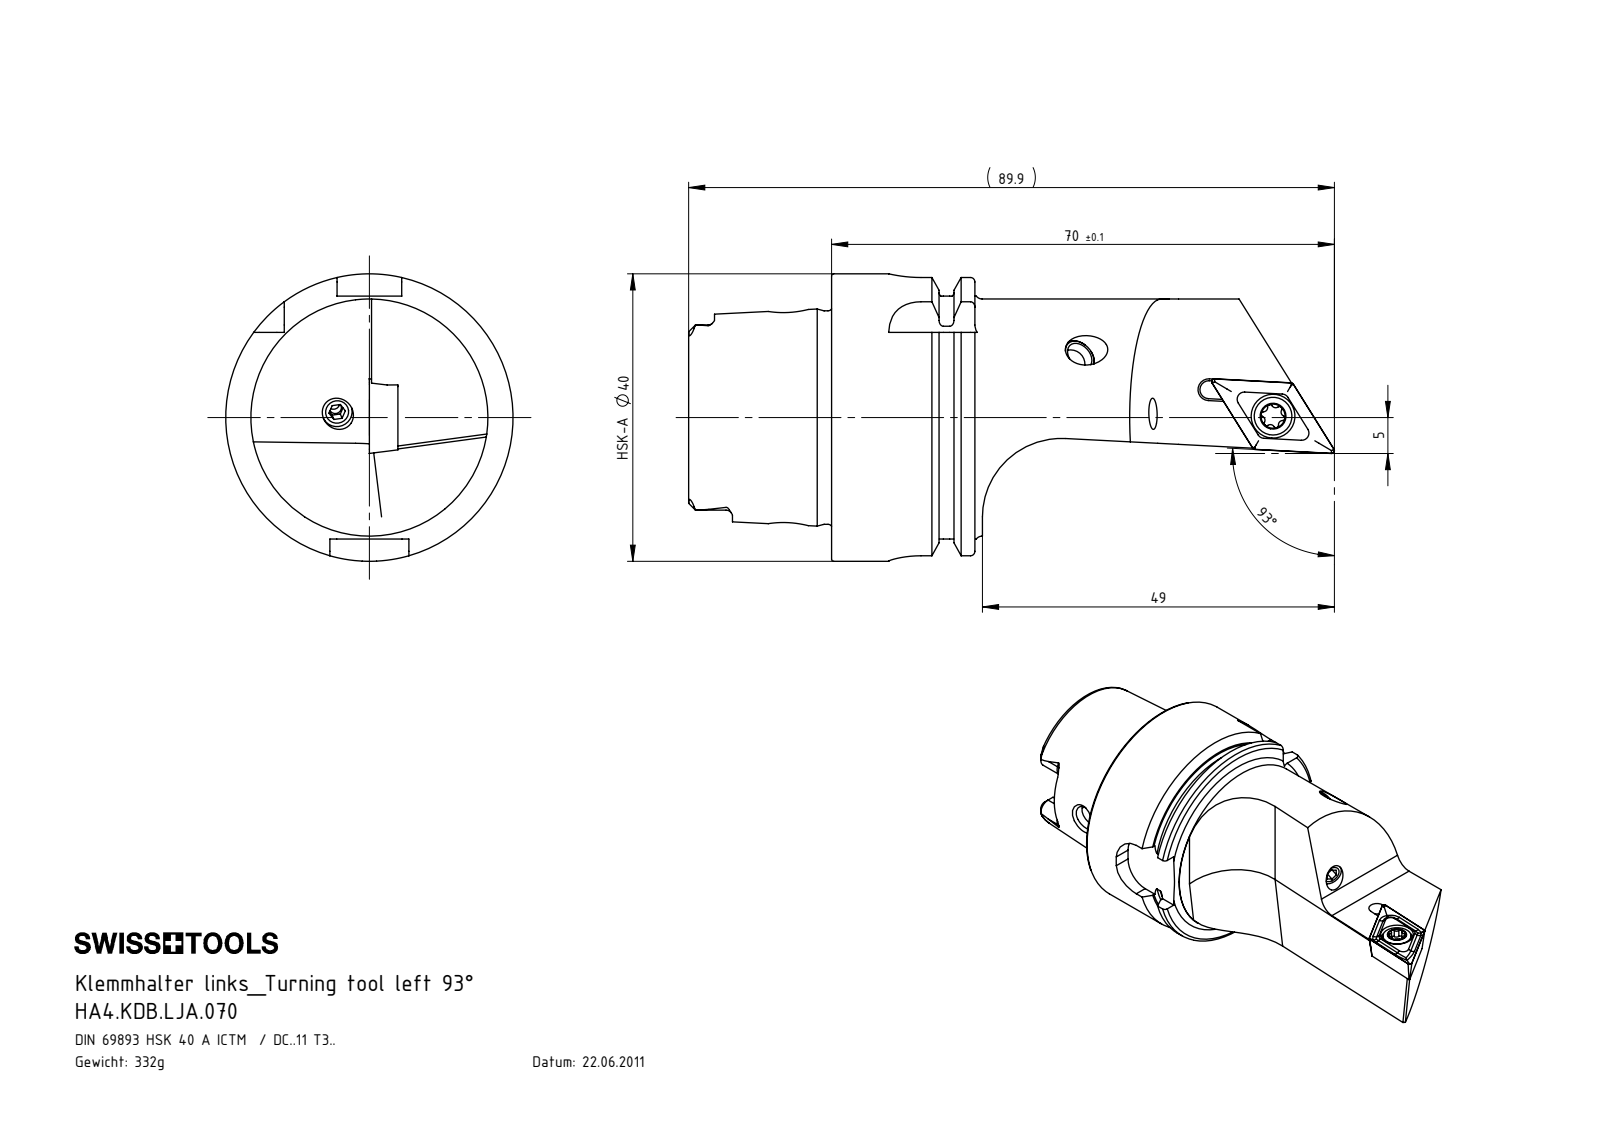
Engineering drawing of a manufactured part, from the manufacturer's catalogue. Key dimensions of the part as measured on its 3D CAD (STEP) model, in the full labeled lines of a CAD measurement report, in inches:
Part name (STEP PRODUCT): WCB-ER2.001.009_A; HA4-KDB.LJA.070_C_Fertigbearbeitung; KVT_MB_600_050; WKX-ER1.004.005_A_PreviewCfg (+2 more)
STEP written by: SolidWorks 2017 (AUTOMOTIVE_DESIGN)
Units: inches
Bodies: 6 solids, 248 faces (88 planar, 61 cylindrical, 99 other)
Overall size (bounding box): 3.54 × 1.575 × 1.575
Volume: 2.565 in³ · Surface area: 22.11 in²
Round holes (diameter × count): ⌀0.13 ×2, ⌀0.157 ×2, ⌀0.165 ×2, ⌀0.067 ×1, ⌀0.173 ×1, ⌀0.181 ×1, ⌀0.197 ×1, ⌀0.24 ×1, ⌀0.394 ×1, ⌀0.433 ×1, ⌀0.492 ×1, ⌀0.827 ×1
Round bosses / shafts (diameter × count): ⌀0.157 ×2, ⌀1.575 ×1, ⌀1.368 ×1, ⌀1.299 ×1, ⌀1.17 ×1, ⌀0.207 ×1, ⌀0.197 ×1
Partial cylindrical surfaces — rounded edges, fillets, slot ends (radius × count): R0.013 ×6, R0.023 ×6, R0.035 ×6, R0.074 ×4, R0.177 ×4, R0.049 ×1, R0.118 ×1, R0.433 ×1
Main face-to-face distances: 0.313, 0.785, 0.472, 0.144, 0.783, 1.096, 1.569, 1.406, 0.622, 0.309
Hole centre spacings: 2.14, 2.144
